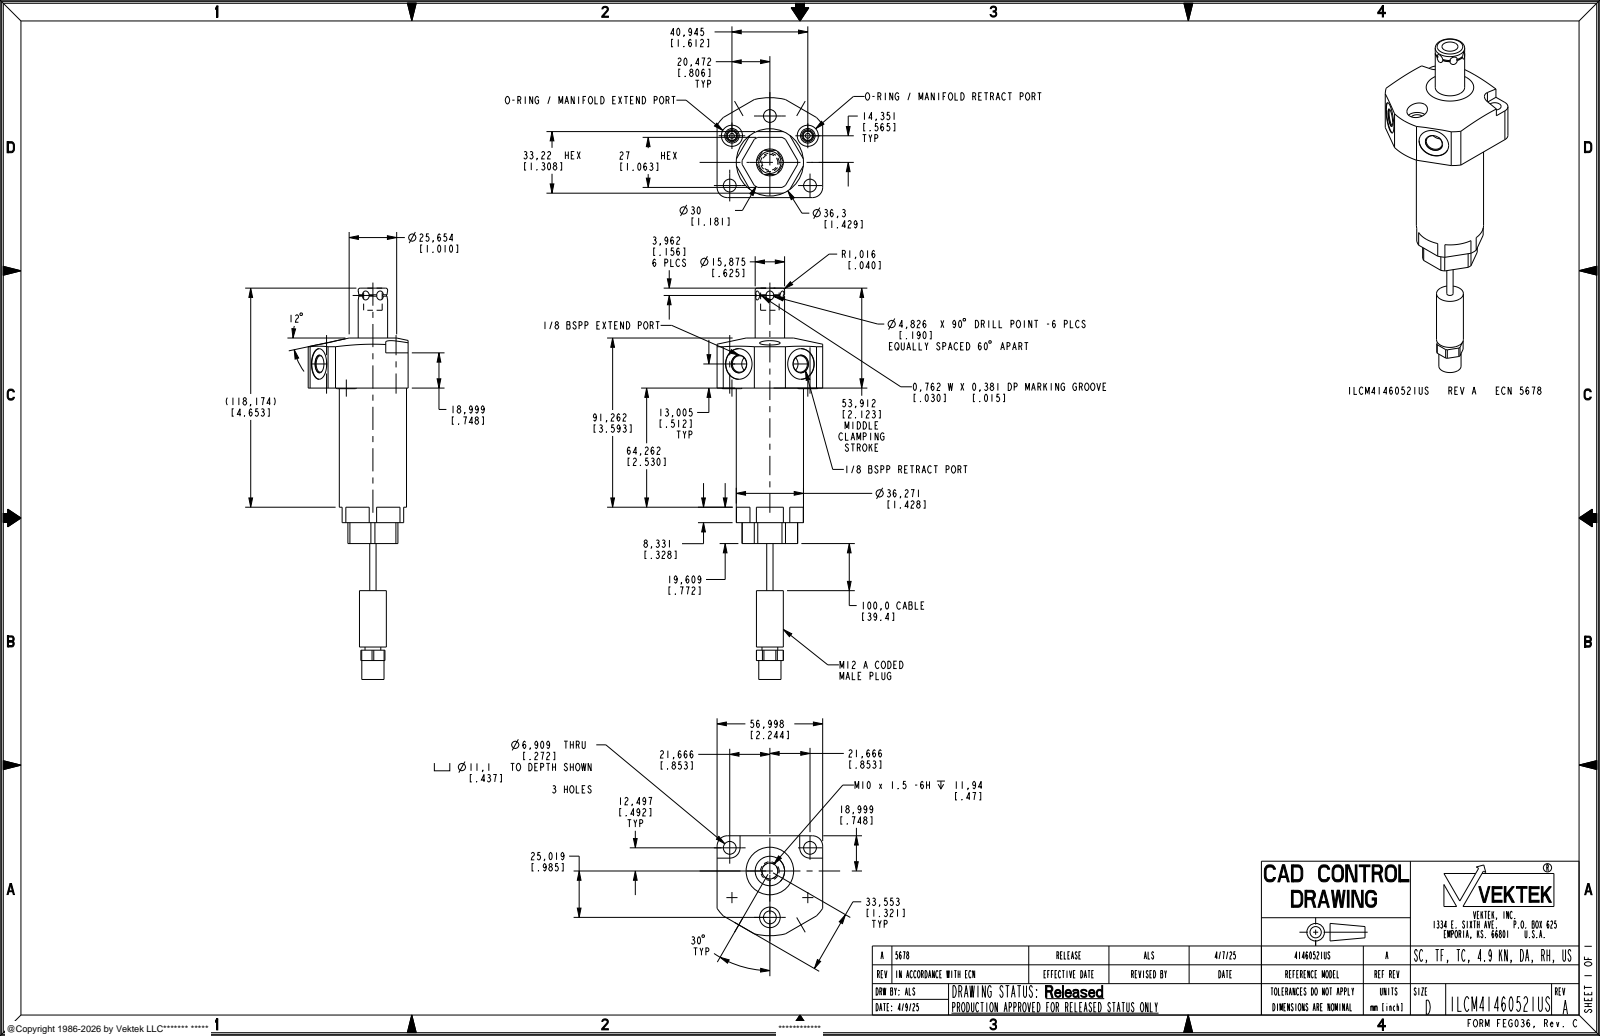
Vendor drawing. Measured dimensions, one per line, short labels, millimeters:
name: ILCM41460521US
written by: CREO PARAMETRIC BY PTC INC, 2021164 (AUTOMOTIVE_DESIGN)
unit: mm
bodies: 1 solid, 198 faces (89 planar, 75 cylindrical, 34 other)
size: 211.09 × 62.08 × 60.27
volume: 157 001 mm³; area: 27 138 mm²
holes: 3× ⌀6.91, 2× ⌀2.49, 2× ⌀6.5, 2× ⌀8.84, 2× ⌀11.4, 2× ⌀16.51, 1× ⌀8.61, 1× ⌀11.1
bosses: 2× ⌀5.49, 1× ⌀36.27, 1× ⌀15.88, 1× ⌀14.5, 1× ⌀11.99, 1× ⌀10.01, 1× ⌀8.51, 1× ⌀3.4
rounds: 2× R5.55, 2× R5.56, 1× R7.56, 1× R15, 1× R34.92
face distances: 27, 57, 3.11, 30.11, 83.87, 33.22, 110.87, 11.28, 72.59, 99.59
hole spacings: 25.02, 23.08, 25, 26.88, 43.33, 49.97, 40.94, 43.34
